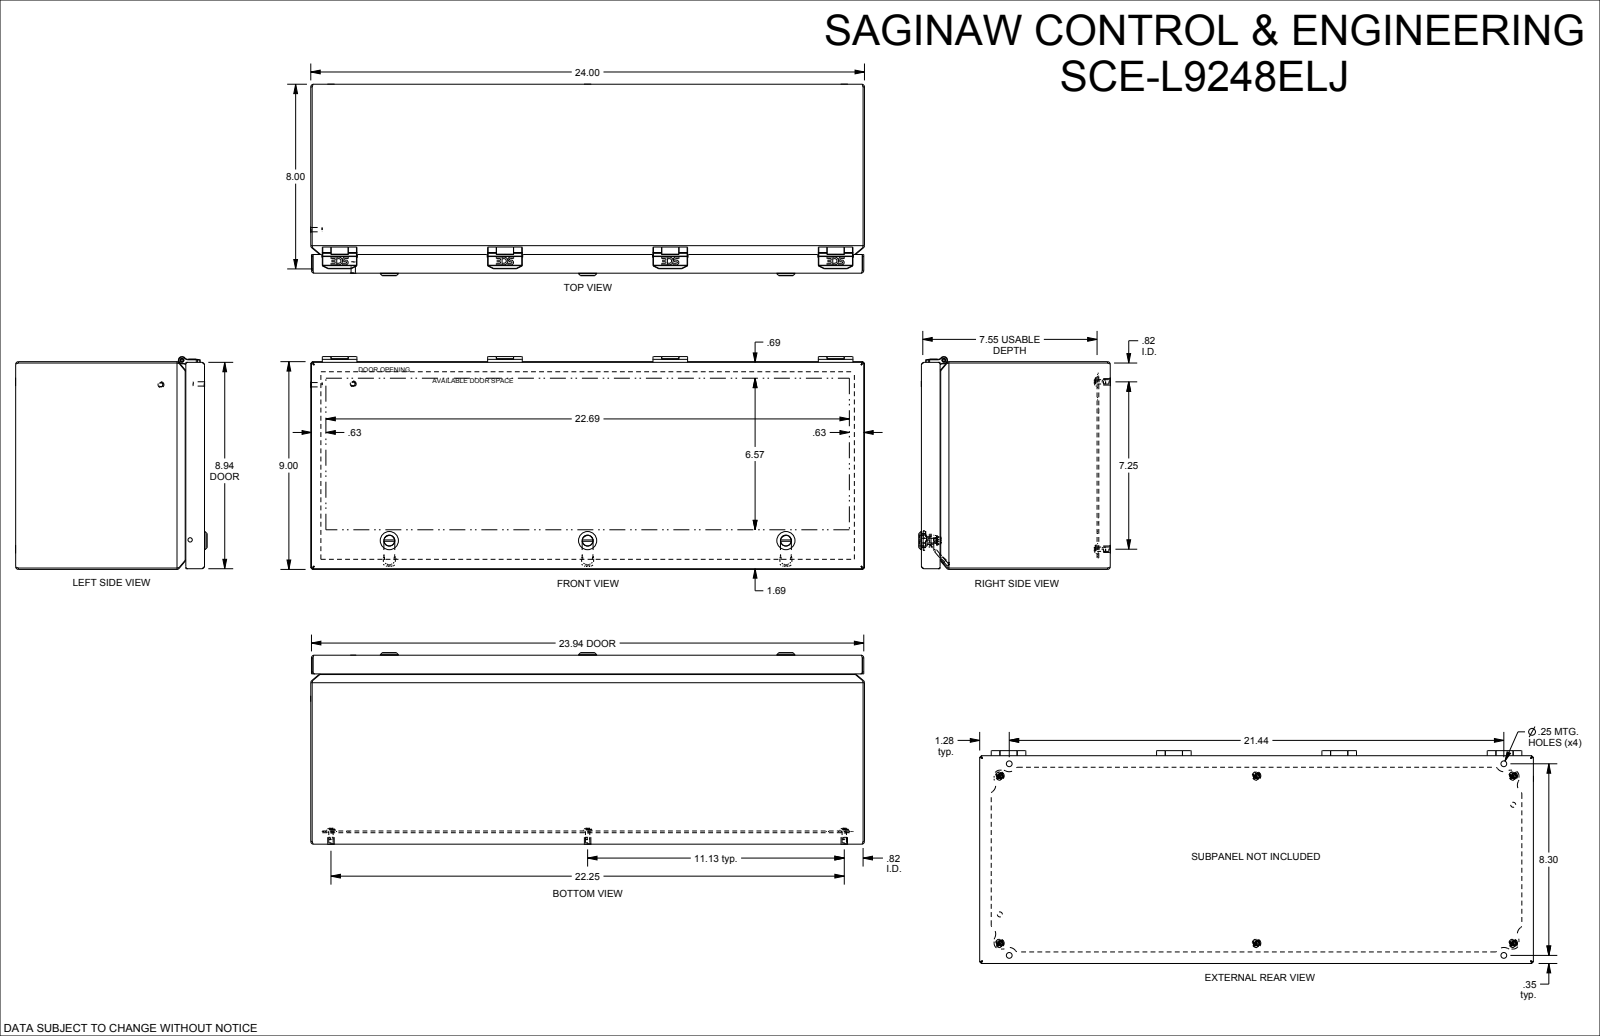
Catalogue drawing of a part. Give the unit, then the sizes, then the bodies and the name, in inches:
Units: inches
Overall size (bounding box): 24.004 × 9.22 × 8.296
Round holes (diameter × count): ⌀0.19 ×6, ⌀0.25 ×6, ⌀0.284 ×6, ⌀0.164 ×4, ⌀0.174 ×4, ⌀0.266 ×4, ⌀0.338 ×4, ⌀0.2 ×3, ⌀0.239 ×3, ⌀0.254 ×3, ⌀0.269 ×3, ⌀0.282 ×3
Round bosses / shafts (diameter × count): ⌀0.188 ×8, ⌀0.373 ×6, ⌀0.28 ×6, ⌀0.26 ×4, ⌀0.15 ×4, ⌀0.788 ×3, ⌀0.548 ×3, ⌀0.46 ×3
Partial cylindrical surfaces — rounded edges, fillets, slot ends (radius × count): R0.008 ×64, R0.02 ×58, R0.01 ×18, R0.05 ×16, R0.125 ×13, R0.25 ×13, R0.063 ×11, R0.06 ×10
Main face-to-face distances: 0.059, 8.941, 8.125, 8.066, 8.185, 8.126, 0.06, 0.437, 0.571, 0.512
Hole centre spacings: 7.167, 14.333, 11.125, 7.167, 21.5, 7.25, 7.251, 13.279
Volume: 79.74 in³ · Surface area: 2 516 in²
Bodies: 56 solids, 2520 faces (1278 planar, 644 cylindrical, 598 other)
Part name (STEP PRODUCT): SCE-L9248ELJ
STEP written by: SolidWorks 2022 (AUTOMOTIVE_DESIGN)
